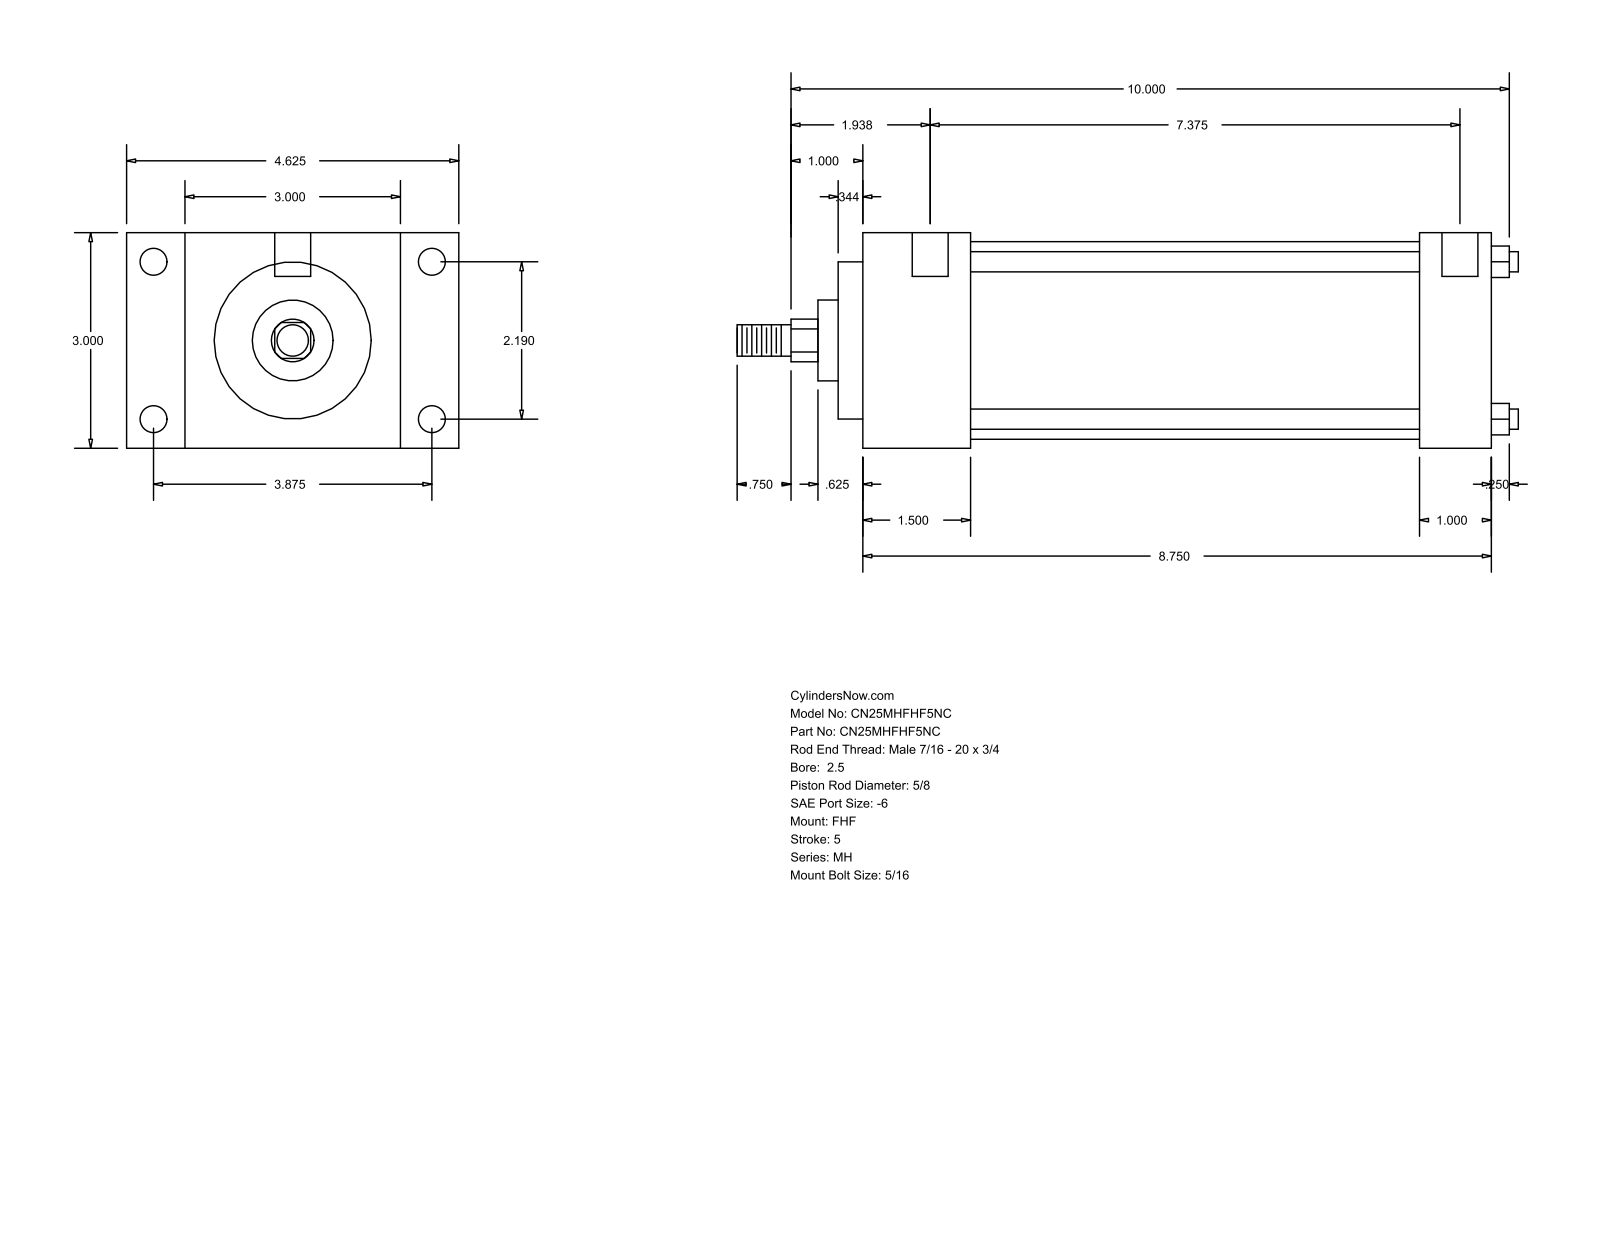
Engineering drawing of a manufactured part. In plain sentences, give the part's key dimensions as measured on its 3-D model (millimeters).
The part is named "MH_FHF__0250_0.625". Its 3-D file was written by "GSSL Pune (CONFIG_CONTROL_DESIGN)". It is 0 solids with 90 faces: 61 planar, 29 cylindrical and 0 other. Overall it measures 276.23 by 117.47 by 76.2 millimeters. Round holes: 4 of diameter 5.56, 4 of diameter 9.53, 2 of diameter 12.7. Round bosses or shafts: 4 of diameter 7.14, 1 of diameter 69.85, 1 of diameter 55.55, 1 of diameter 28.57, 1 of diameter 15.88, 1 of diameter 11.11. Partial cylindrical surfaces (rounded edges, fillets, slot ends): 1 of radius 7.54. The main face-to-face distances are 76.2, 222.25, 38.1, 184.15, 20.64, 96.84, 117.48, 25.4, 196.85, 158.75. The hole center spacings are 55.62, 98.42, 113.05, 195.26, 3.17, 4.76, 187.33, 190.5.
